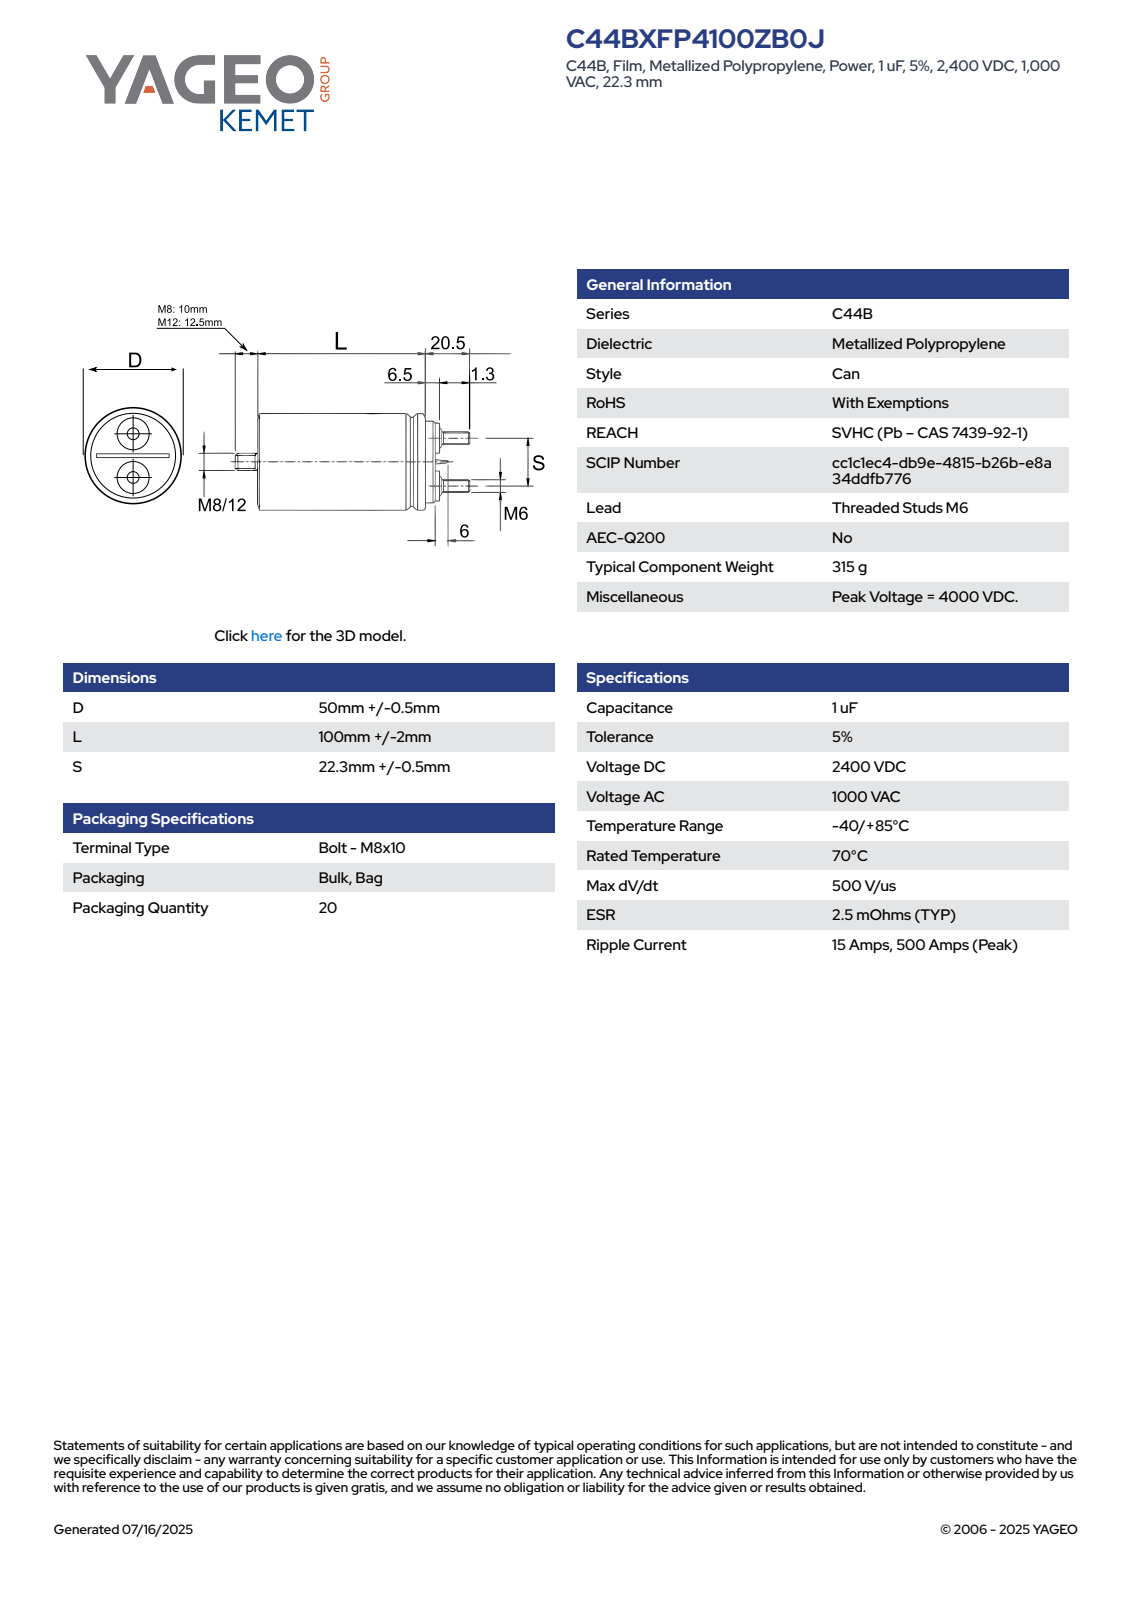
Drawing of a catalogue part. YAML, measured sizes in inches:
part_name: "CFP_M6_50X100_D50.5L102S22.8"
step_written_by: "SolidWorks 2014 (AUTOMOTIVE_DESIGN)"
units: inches
bodies: {solids: 1, faces: 117, planar: 35, cylindrical: 39, other: 43}
overall_size: [5.217, 1.989, 1.988]
volume: 12.8
surface_area: 35.12
round_bosses_or_shafts:
  - {diameter: 0.546, count: 2}
  - {diameter: 0.394, count: 2}
  - {diameter: 0.236, count: 2}
  - {diameter: 1.988, count: 1}
  - {diameter: 1.759, count: 1}
  - {diameter: 0.315, count: 1}
partial_cylinders:
  - {radius: 0.014, count: 1}
  - {radius: 0.994, count: 1}
face_to_face_distances: [4.173, 4.016, 0.157, 0.028, 4.272, 0.256, 0.098, 4.311, 0.295, 0.138]
